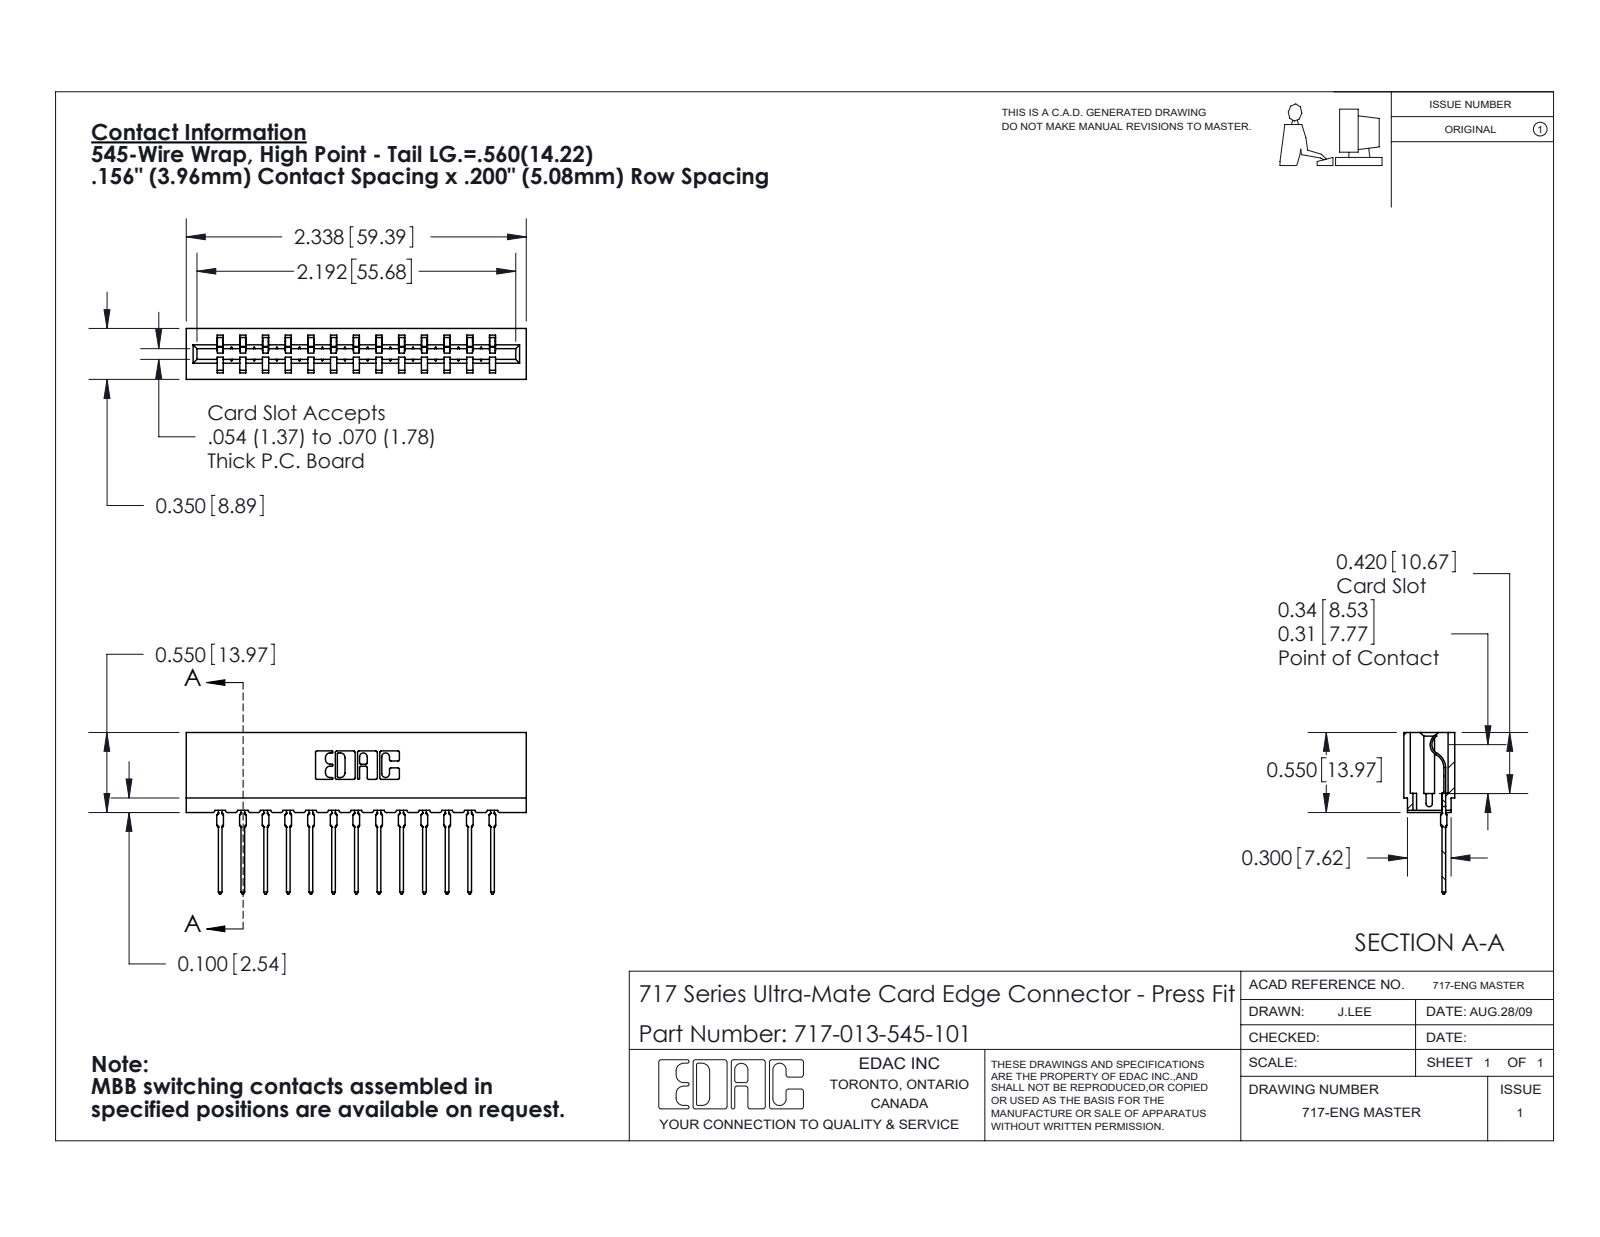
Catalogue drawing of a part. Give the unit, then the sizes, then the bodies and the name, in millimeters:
Units: millimetres
Overall size (bounding box): 59.4 × 28.2 × 8.9
Partial cylindrical surfaces — rounded edges, fillets, slot ends (radius × count): R0.4 ×26, R0.5 ×26, R0.3 ×22, R0.2 ×6, R0.8 ×6, R0.1 ×4, R0.3 ×4, R0.7 ×3
Main face-to-face distances: 5.4, 3.5, 4, 8.9, 15.8, 11.9, 7.9, 5, 1.9, 1.1
Volume: 5 180 mm³ · Surface area: 7 168 mm²
Bodies: 14 solids, 1563 faces (938 planar, 287 cylindrical, 338 other)
Part name (STEP PRODUCT): 717 Part_Insulator Option - 06; 717-013-545-101; 745-292-001_545
STEP written by: SolidWorks 2020 (CONFIG_CONTROL_DESIGN)
